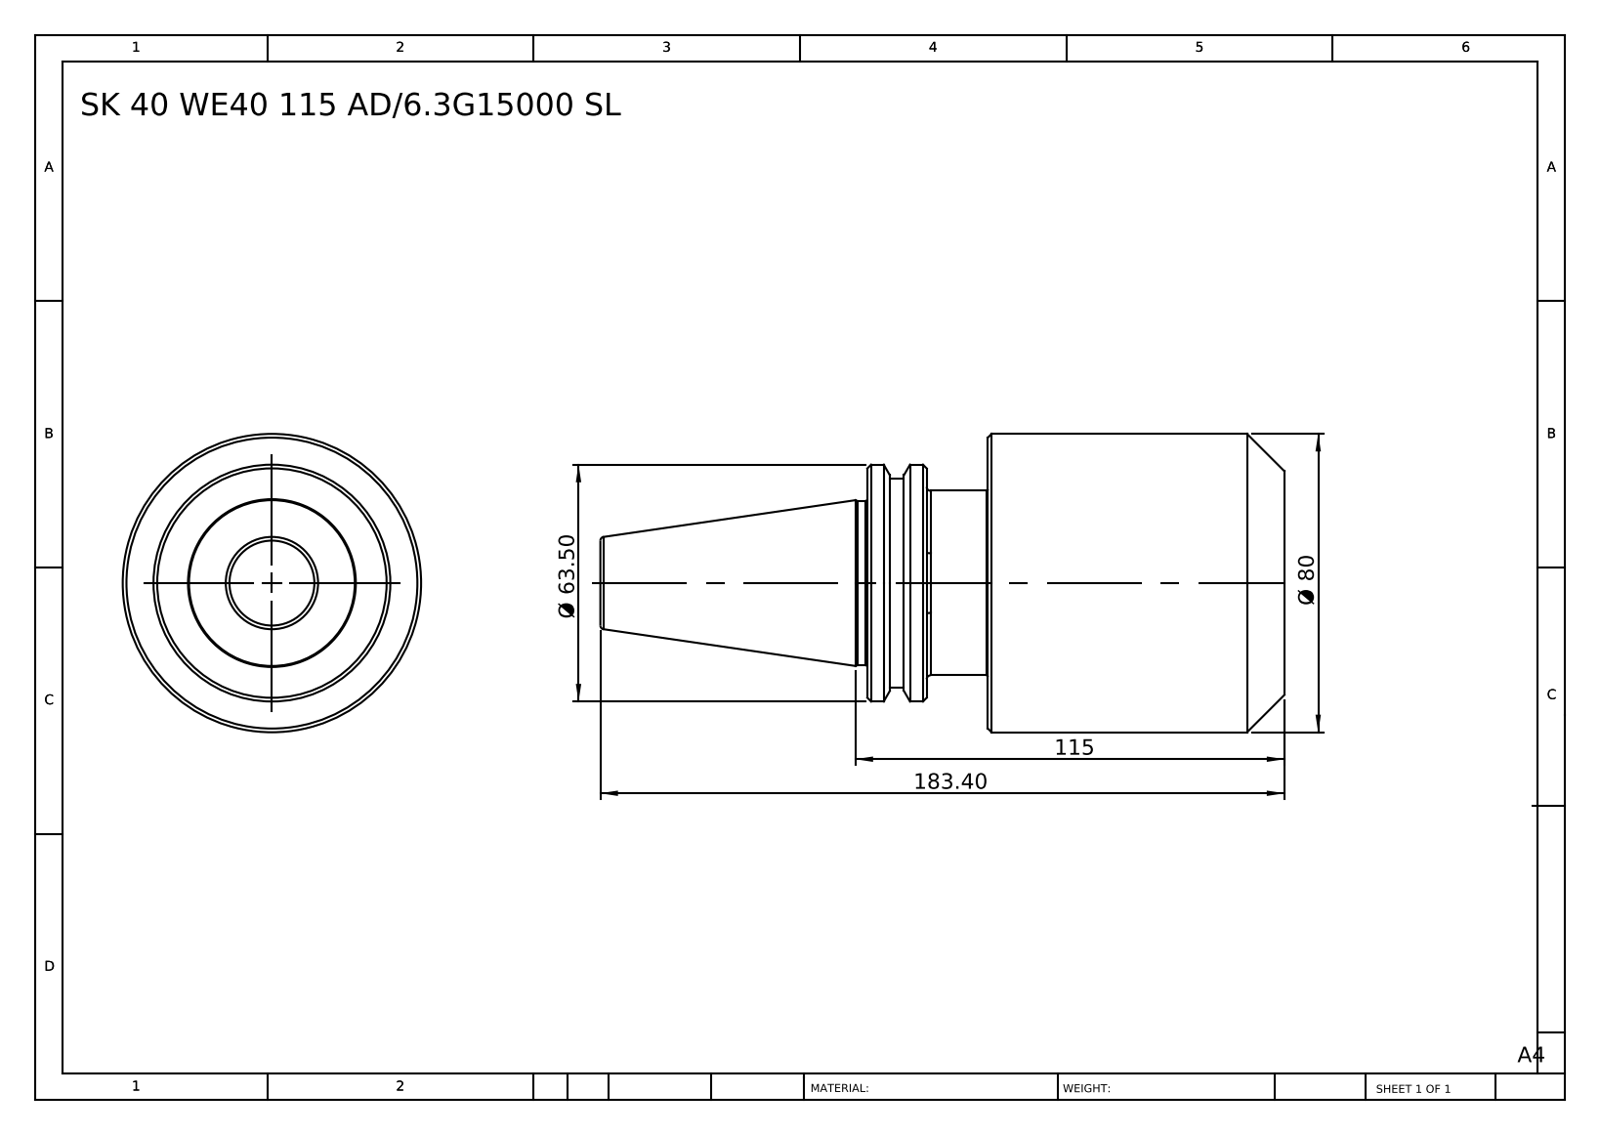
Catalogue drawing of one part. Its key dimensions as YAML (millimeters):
part_name: "SK40 WE40 115 AD-6.3G15000 SL"
step_written_by: "SolidWorks 2014 (CONFIG_CONTROL_DESIGN)"
units: millimeters
bodies: {solids: 1, faces: 44, planar: 8, cylindrical: 12, other: 24}
overall_size: [183.4, 80, 80]
volume: 536664
surface_area: 43837
round_bosses_or_shafts:
  - {diameter: 80, count: 1}
  - {diameter: 63.5, count: 1}
  - {diameter: 56, count: 1}
  - {diameter: 49.5, count: 1}
  - {diameter: 44, count: 1}
face_to_face_distances: [79.5, 111.8, 32.3, 95.9, 16.4, 15.9, 183.4, 103.9, 87.5, 71.6]
